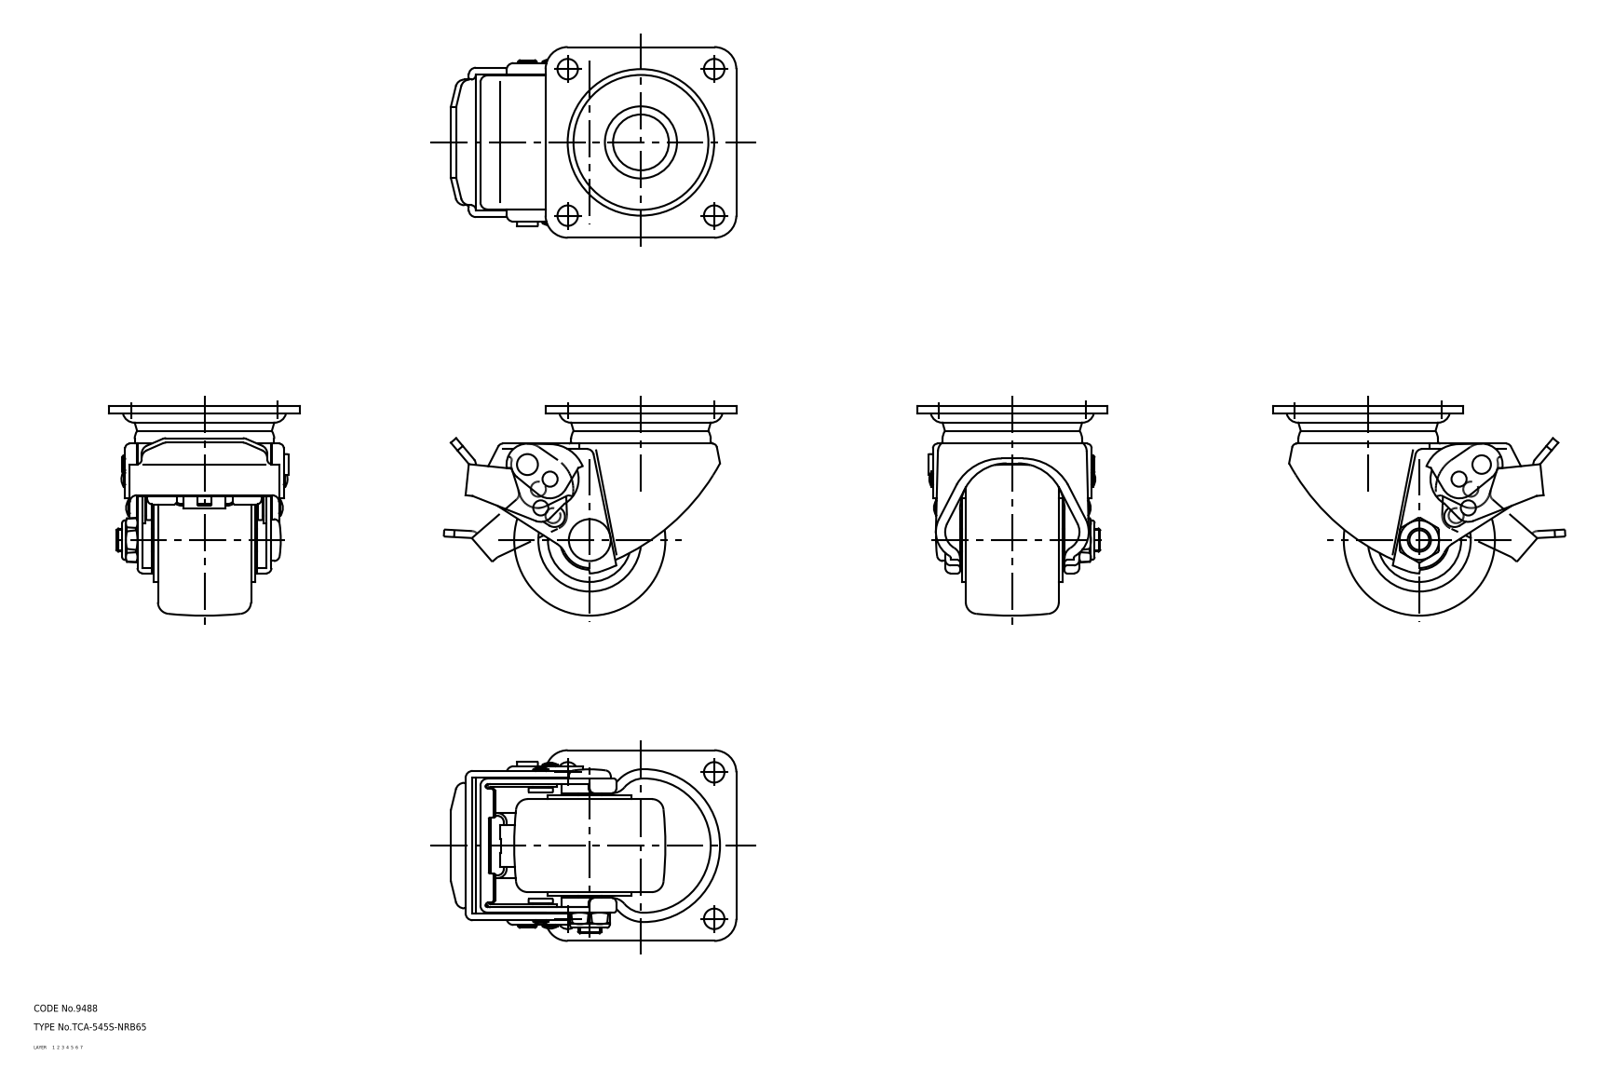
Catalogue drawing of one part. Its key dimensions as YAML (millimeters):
part_name: "lever; main shaft; wheel; mounting plate (+2 more)"
step_written_by: "CADfix (AUTOMOTIVE_DESIGN)"
units: millimeters
bodies: {solids: 6, faces: 468, planar: 0, cylindrical: 0, other: 468}
overall_size: [122.73, 90, 82]
volume: 259021
surface_area: 86233
